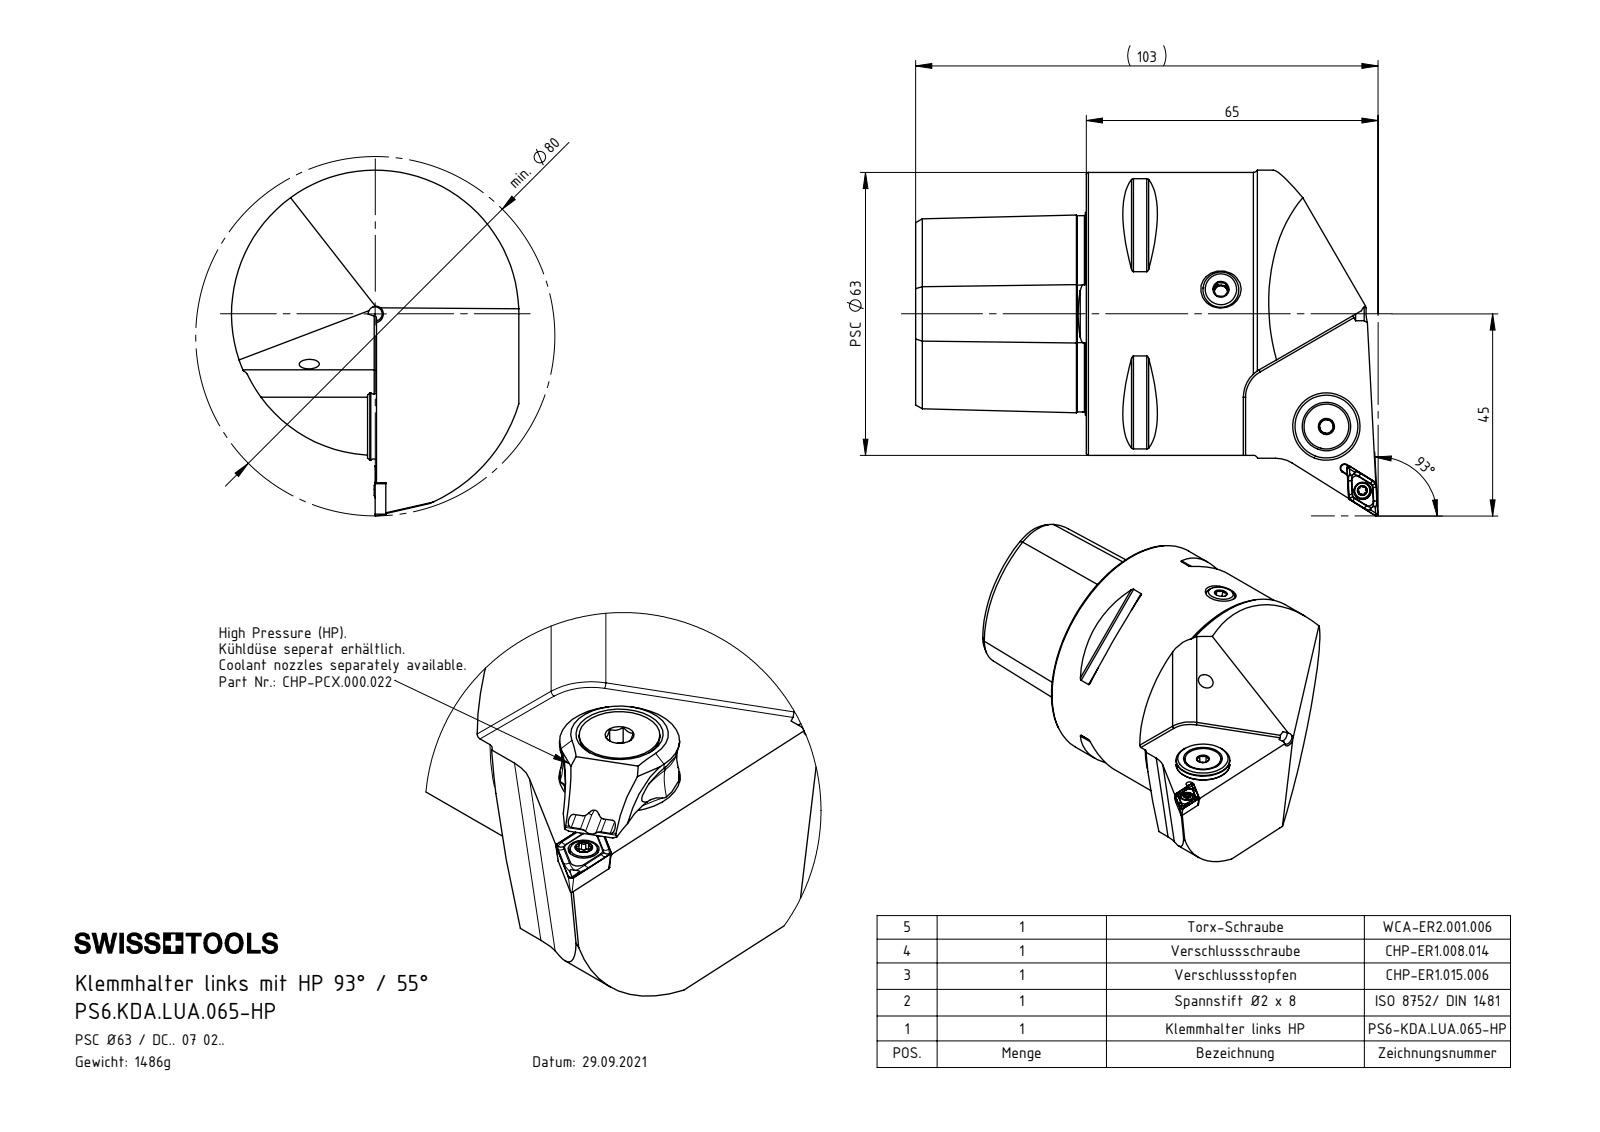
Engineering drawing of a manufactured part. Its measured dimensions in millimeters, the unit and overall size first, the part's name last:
Units: millimetres
Overall size (bounding box): 103 × 77 × 64
Round holes (diameter × count): ⌀4.2 ×3, ⌀1.2 ×1, ⌀2 ×1, ⌀2.05 ×1, ⌀2.8 ×1, ⌀3 ×1, ⌀3.85 ×1, ⌀5 ×1, ⌀5.3 ×1, ⌀7 ×1, ⌀8.1 ×1, ⌀10 ×1
Round bosses / shafts (diameter × count): ⌀63 ×1, ⌀14.85 ×1, ⌀13.4 ×1, ⌀10 ×1, ⌀8 ×1, ⌀5.5 ×1, ⌀5 ×1, ⌀3.4 ×1
Partial cylindrical surfaces — rounded edges, fillets, slot ends (radius × count): R0.5 ×12, R1 ×8, R0.21 ×6, R0.36 ×4, R6 ×4, R0.36 ×2, R1.1 ×2, R1.2 ×2
Main face-to-face distances: 38, 31.7, 24.88, 11, 27, 73, 46, 35, 55.8, 4.5
Hole centre spacings: 4.5, 13.2, 13.3, 16.34, 16.45, 27.5, 48.49, 52.92
Volume: 189 781 mm³ · Surface area: 32 866 mm²
Bodies: 9 solids, 484 faces (106 planar, 134 cylindrical, 244 other)
Part name (STEP PRODUCT): ISO 8752 2x8; PS6-KDA.LUA.065-HP_A; WCA-ER2.001.006_A; PS6.KDA.LUA.065-HP (+7 more)
STEP written by: SolidWorks 2022 (CONFIG_CONTROL_DESIGN)
